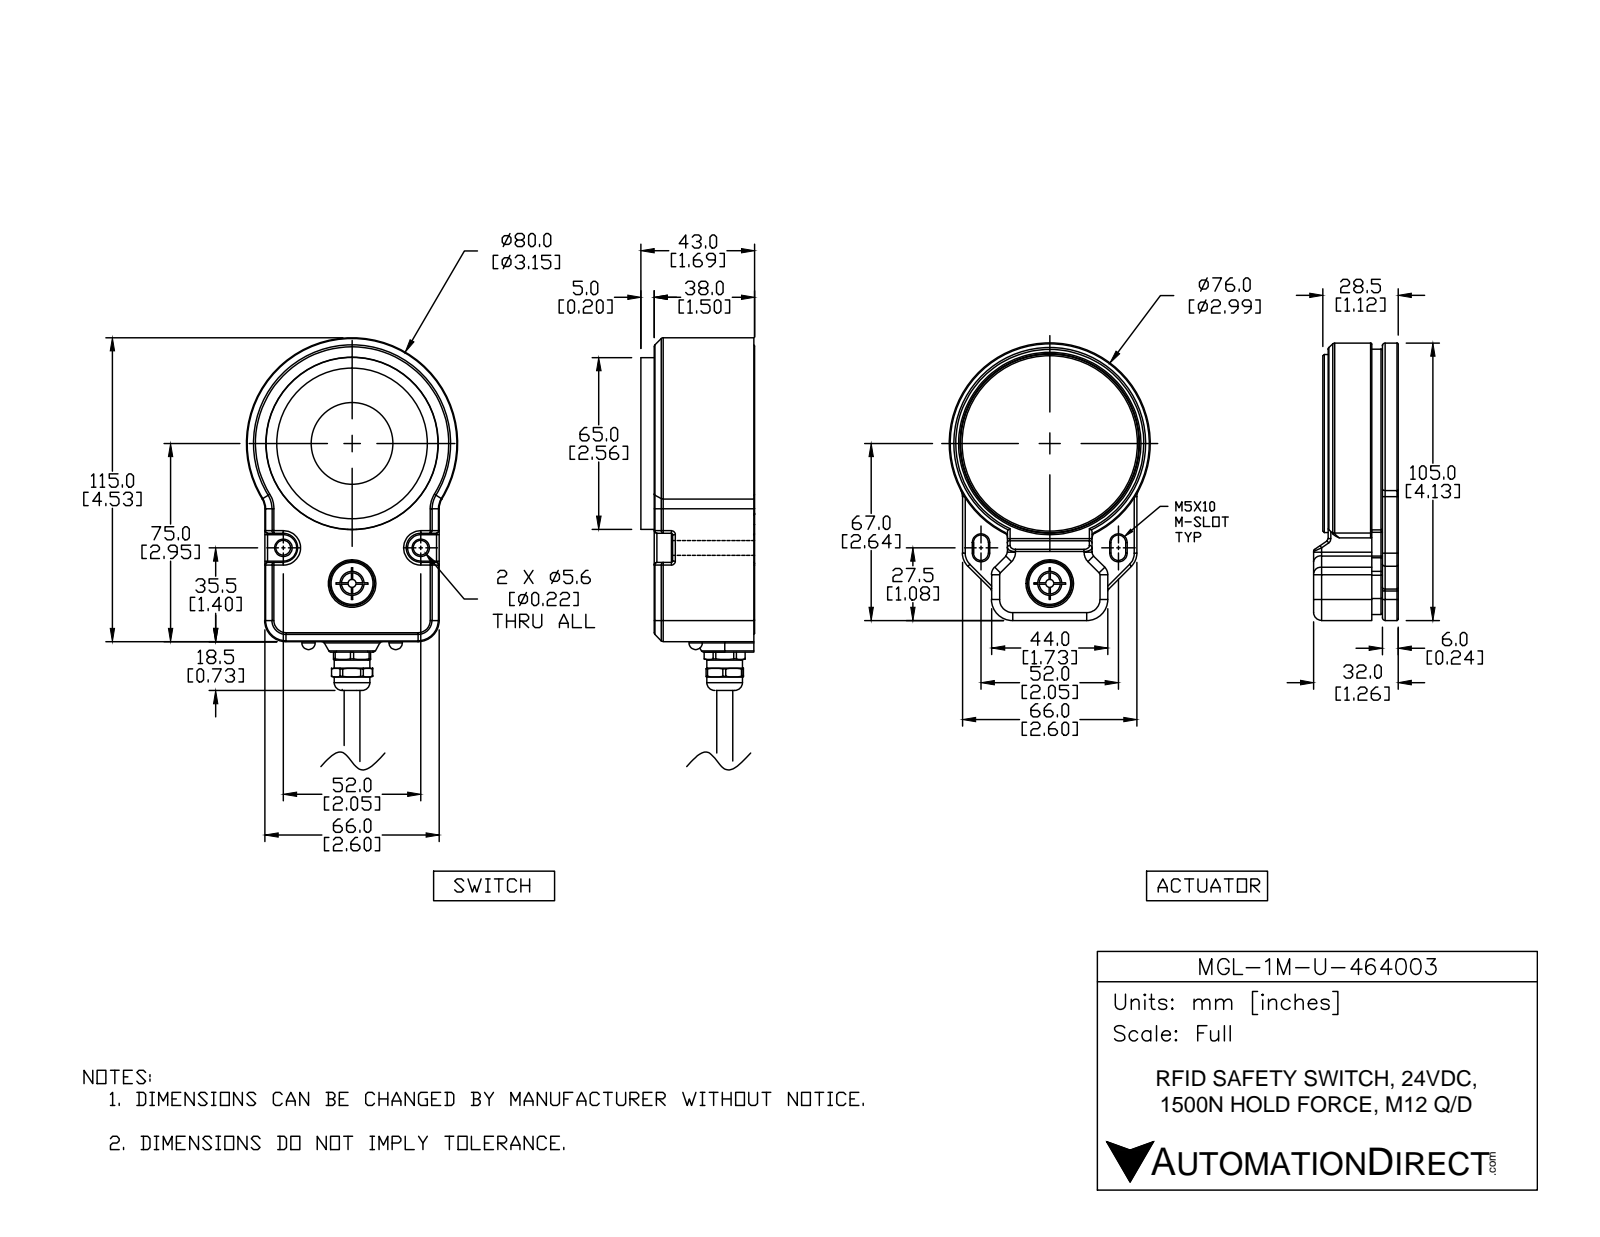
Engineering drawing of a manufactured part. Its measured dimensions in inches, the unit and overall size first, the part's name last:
Units: inches
Overall size (bounding box): 8.163 × 3.15 × 2.85
Round holes (diameter × count): ⌀0.098 ×8, ⌀0.13 ×6, ⌀0.197 ×6, ⌀0.453 ×5, ⌀0.157 ×3, ⌀0.315 ×3, ⌀0.354 ×3, ⌀0.22 ×2, ⌀0.276 ×2, ⌀0.374 ×2, ⌀0.465 ×2, ⌀0.252 ×1
Round bosses / shafts (diameter × count): ⌀0.02 ×4, ⌀0.079 ×3, ⌀0.472 ×2, ⌀0.228 ×2, ⌀0.213 ×2, ⌀0.047 ×2, ⌀2.992 ×1, ⌀2.811 ×1
Partial cylindrical surfaces — rounded edges, fillets, slot ends (radius × count): R0.02 ×186, R0.039 ×86, R0.079 ×26, R0.012 ×17, R0.118 ×13, R0.157 ×9, R0.217 ×8, R0.024 ×7
Main face-to-face distances: 0.315, 0.236, 2.299, 1.378, 0.118, 2.614, 0.413, 2.201, 2.85, 0.65
Hole centre spacings: 1.392, 1.969, 0.984, 1.28, 1.537, 0.787, 1.364, 0.349
Volume: 19.31 in³ · Surface area: 219.5 in²
Bodies: 19 solids, 1753 faces (428 planar, 743 cylindrical, 582 other)
Part name (STEP PRODUCT): MGL-1M-U-464003; MGL-1M-U-464003_1; MGL-1M-U-464003_2
STEP written by: SolidWorks 2017 (AUTOMOTIVE_DESIGN)
